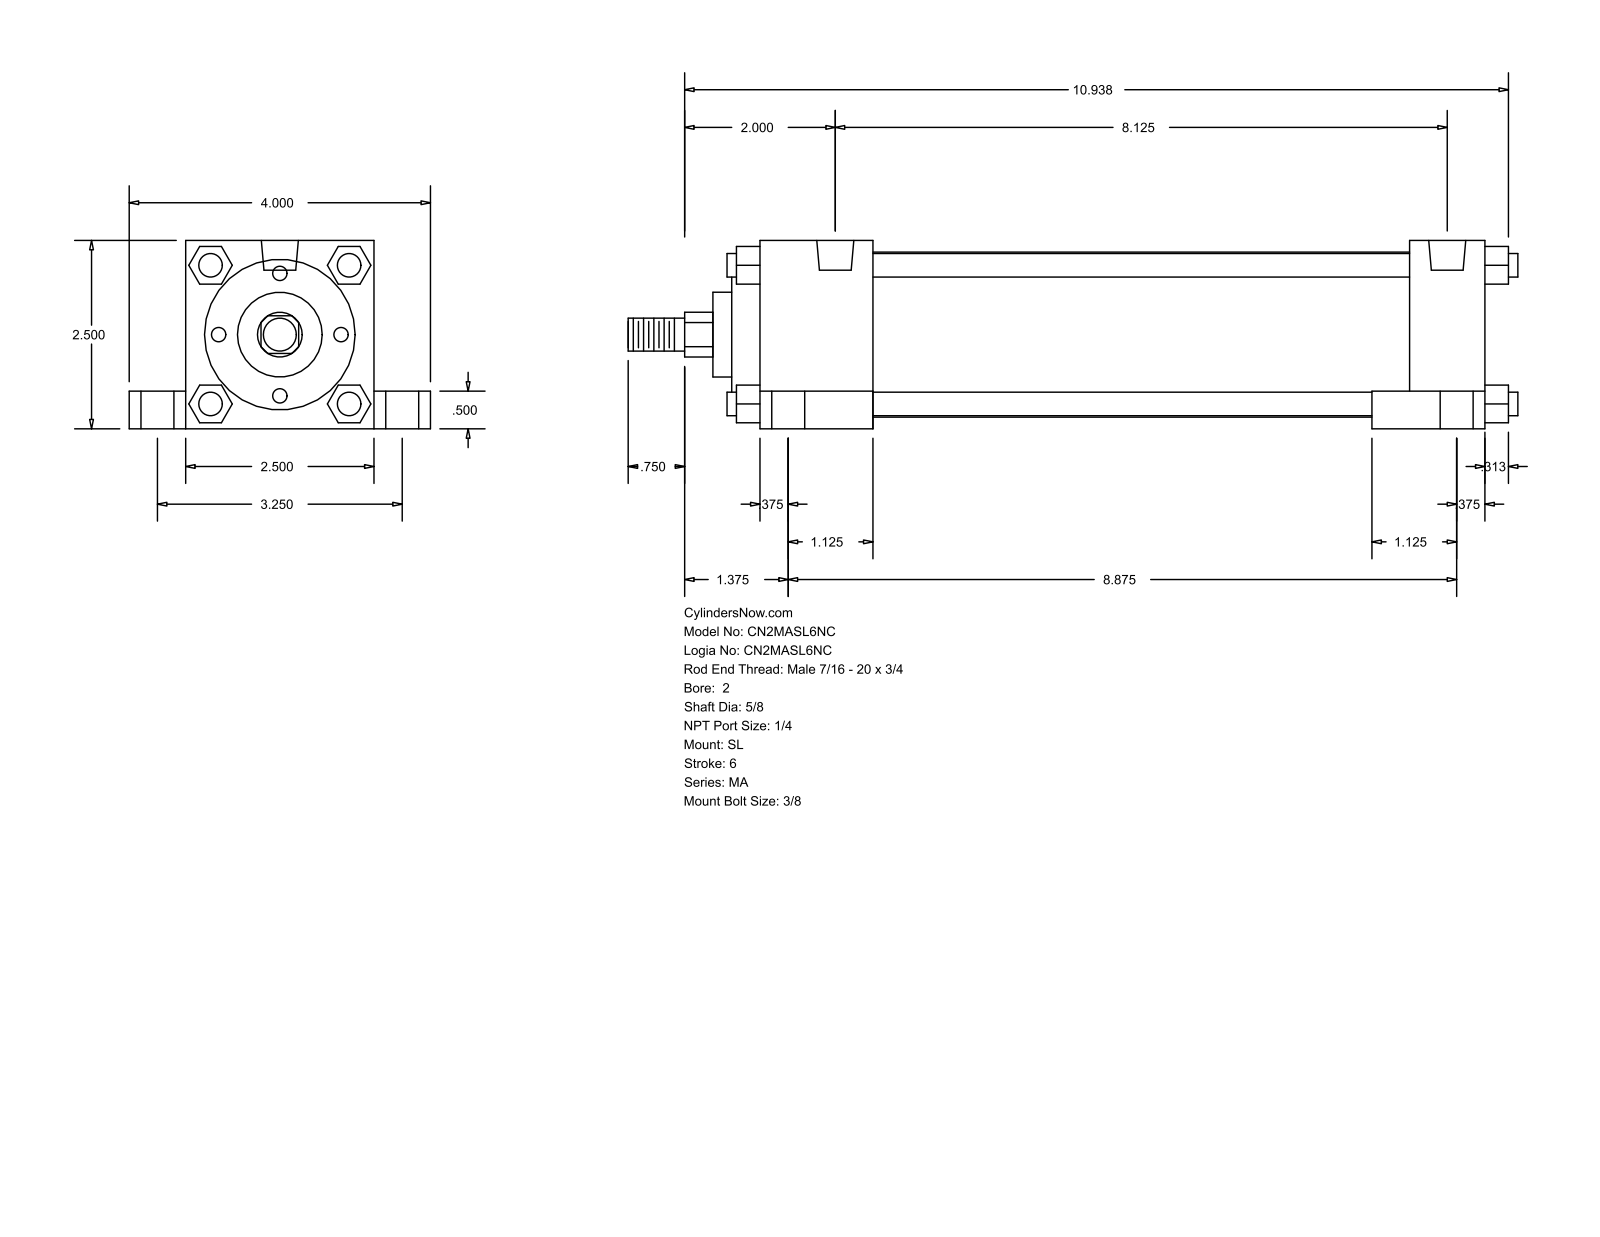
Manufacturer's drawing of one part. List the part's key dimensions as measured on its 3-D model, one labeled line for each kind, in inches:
Part name (STEP PRODUCT): MA_SL__0200_0.625
STEP written by: GSSL Pune (CONFIG_CONTROL_DESIGN)
Units: inches
Bodies: 0 solids, 150 faces (113 planar, 37 cylindrical, 0 other)
Overall size (bounding box): 11.813 × 4 × 2.5
Round holes (diameter × count): ⌀0.313 ×4, ⌀0.437 ×4, ⌀0.687 ×4, ⌀0.492 ×2
Round bosses / shafts (diameter × count): ⌀0.313 ×4, ⌀2.19 ×1, ⌀2 ×1, ⌀1.125 ×1, ⌀0.625 ×1, ⌀0.437 ×1
Partial cylindrical surfaces — rounded edges, fillets, slot ends (radius × count): R0.297 ×1
Main face-to-face distances: 2.5, 0.5, 0.375, 7.125, 0.75, 3.25, 1.5, 2, 9.625, 8.125
Hole centre spacings: 1.63, 1.741, 3.25, 8.125, 8.409, 8.875, 8.9, 9.452
